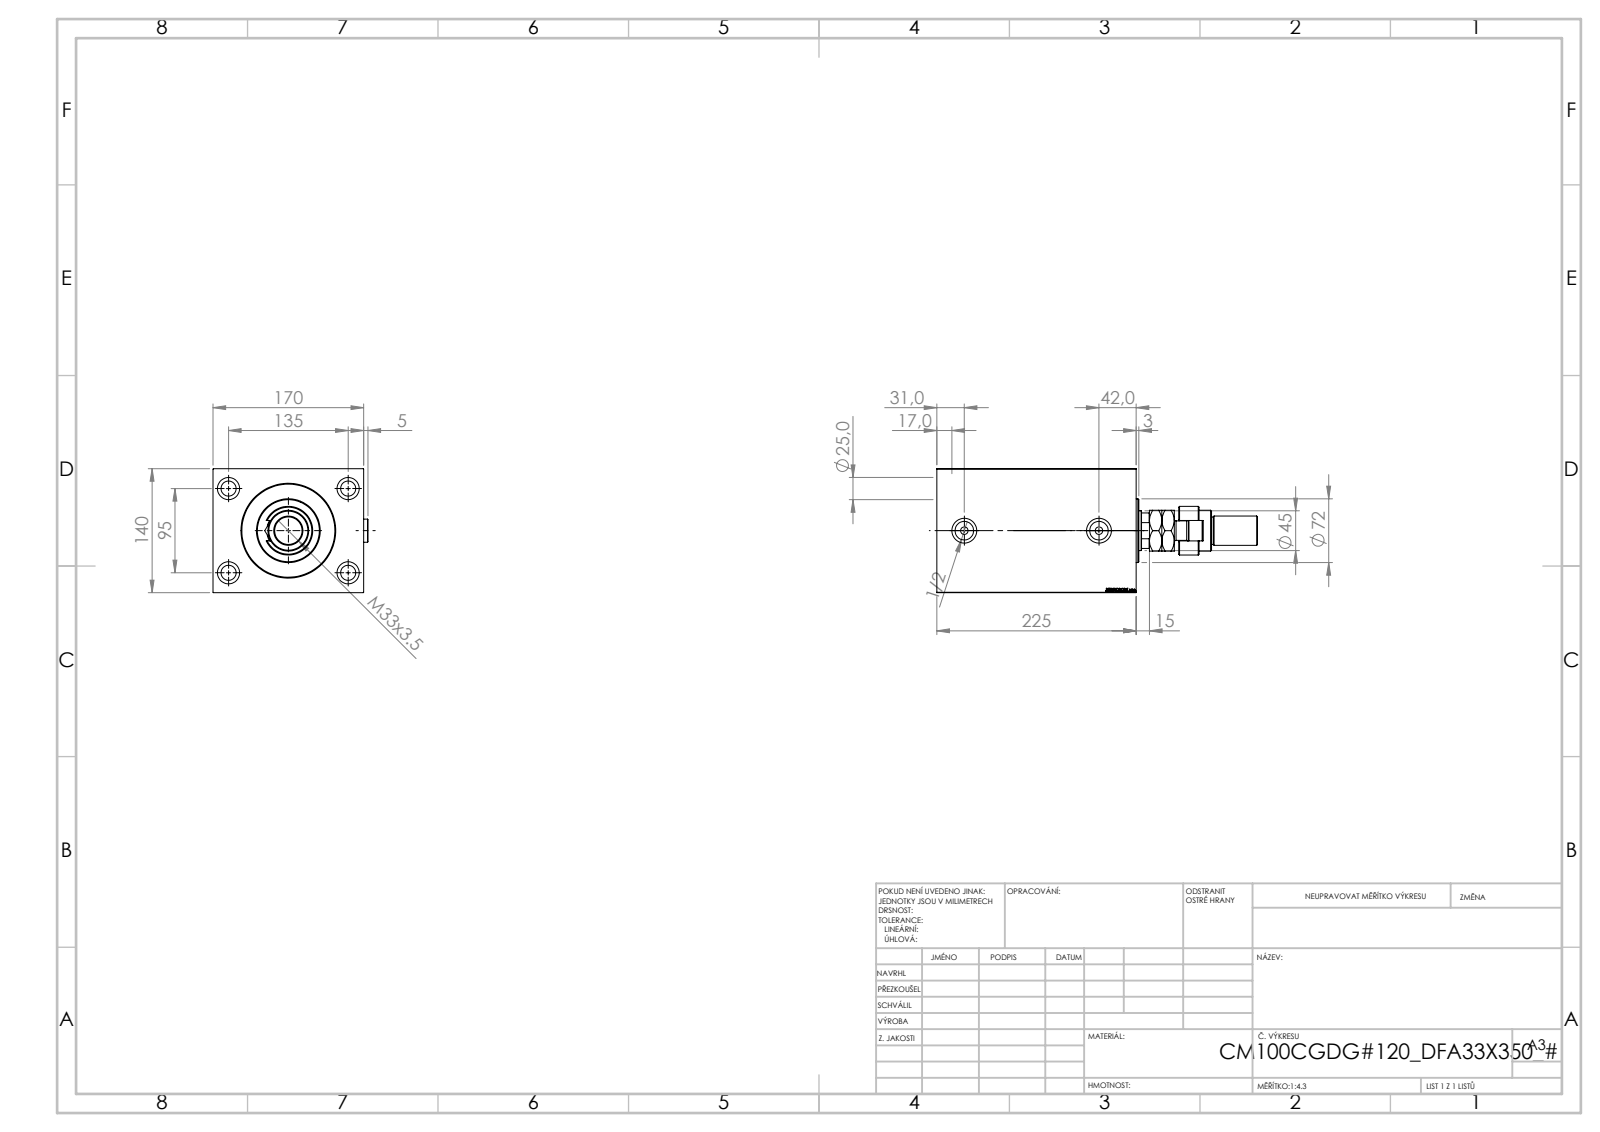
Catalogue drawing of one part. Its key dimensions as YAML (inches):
part_name: "MFA; FEMALE_PART_FOR_DFA; Zatka_OIL_PORT; V450CM_C_Body (+2 more)"
step_written_by: "SolidWorks 2019 (CONFIG_CONTROL_DESIGN)"
units: inches
bodies: {solids: 7, faces: 1004, planar: 471, cylindrical: 91, other: 442}
overall_size: [14.252, 6.886, 5.512]
volume: 274.9
surface_area: 652.8
round_holes:
  - {diameter: 0.669, count: 4}
  - {diameter: 0.984, count: 4}
  - {diameter: 0.335, count: 2}
  - {diameter: 0.825, count: 2}
  - {diameter: 1.102, count: 2}
  - {diameter: 1.24, count: 1}
  - {diameter: 1.535, count: 1}
  - {diameter: 1.772, count: 1}
  - {diameter: 1.909, count: 1}
  - {diameter: 3.937, count: 1}
  - {diameter: 4.016, count: 1}
  - {diameter: 4.134, count: 1}
round_bosses_or_shafts:
  - {diameter: 1.024, count: 2}
  - {diameter: 2.835, count: 1}
  - {diameter: 2.165, count: 1}
  - {diameter: 1.811, count: 1}
  - {diameter: 1.378, count: 1}
  - {diameter: 1.299, count: 1}
  - {diameter: 1.22, count: 1}
  - {diameter: 0.866, count: 1}
partial_cylinders:
  - {radius: 0.453, count: 1}
  - {radius: 0.866, count: 1}
face_to_face_distances: [5.512, 6.693, 8.858, 1.024, 7.835, 0.591, 3.543, 8.268, 2.52, 7.244]
hole_center_spacings: [3.25, 3.74, 5.315, 6.499, 5.984]
